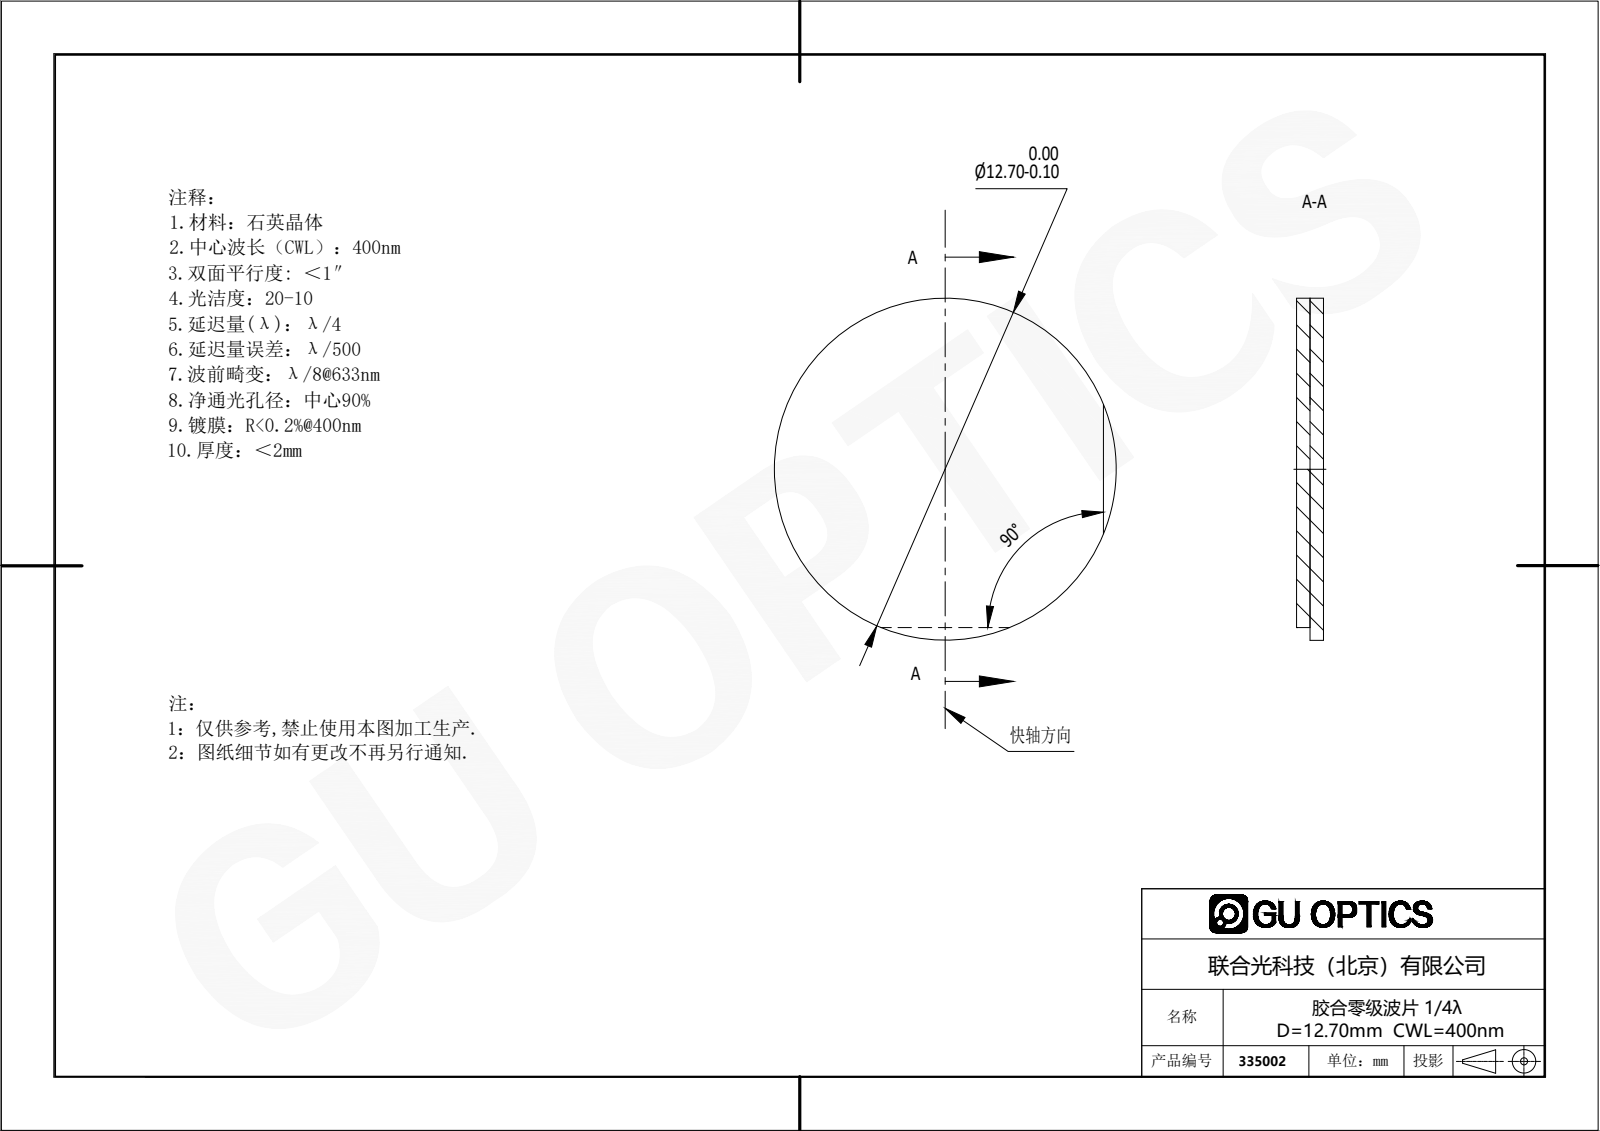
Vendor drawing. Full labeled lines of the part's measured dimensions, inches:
Part name (STEP PRODUCT): 334000
STEP written by: SolidWorks 2019 (AUTOMOTIVE_DESIGN)
Units: inches
Bodies: 2 solids, 12 faces (6 planar, 6 cylindrical, 0 other)
Overall size (bounding box): 0.5 × 0.5 × 0.039
Volume: 0.008 in³ · Surface area: 0.837 in²
Round bosses / shafts (diameter × count): ⌀0.5 ×1
Main face-to-face distances: 0.02, 0.039
